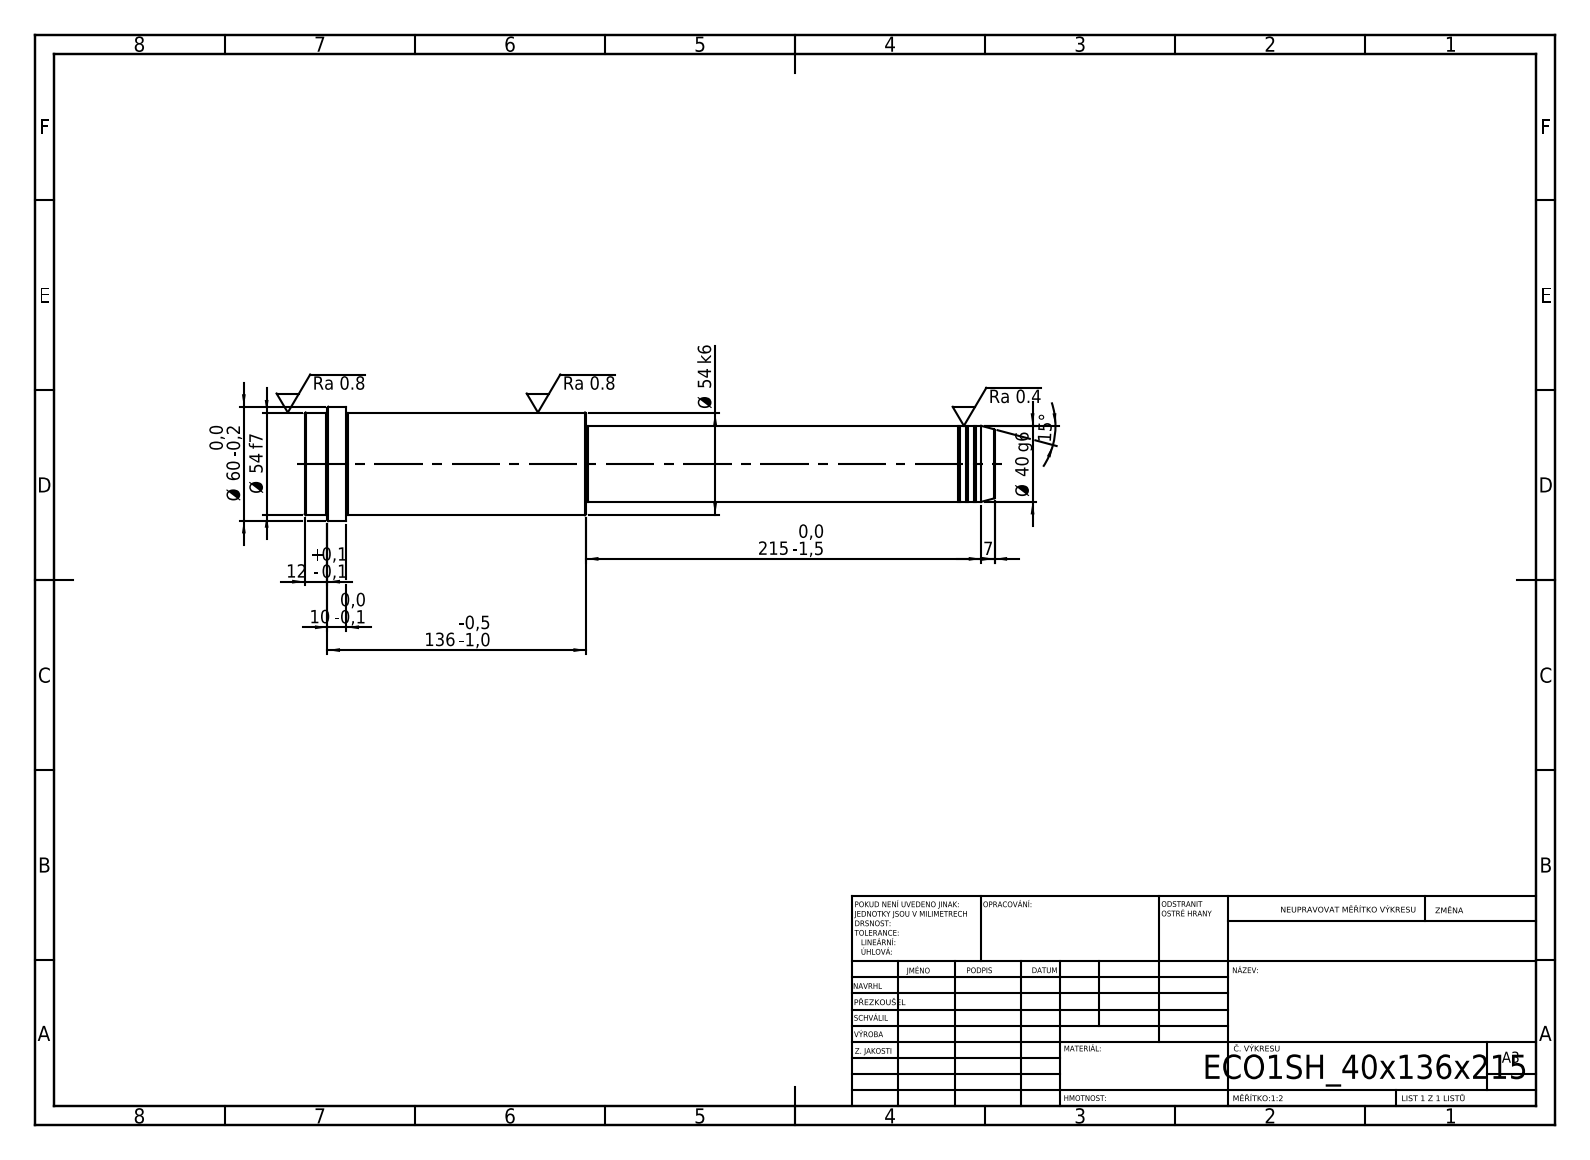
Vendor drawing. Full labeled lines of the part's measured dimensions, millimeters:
STEP written by: SolidWorks 2019 (CONFIG_CONTROL_DESIGN)
Units: millimetres
Bodies: 1 solid, 52 faces (6 planar, 16 cylindrical, 30 other)
Overall size (bounding box): 363 × 60 × 60
Volume: 613 293 mm³ · Surface area: 58 078 mm²
Round bosses / shafts (diameter × count): ⌀60 ×1, ⌀54 ×1, ⌀40 ×1, ⌀39 ×1
Main face-to-face distances: 148, 215, 363, 341, 126, 22, 351, 136, 10, 12
